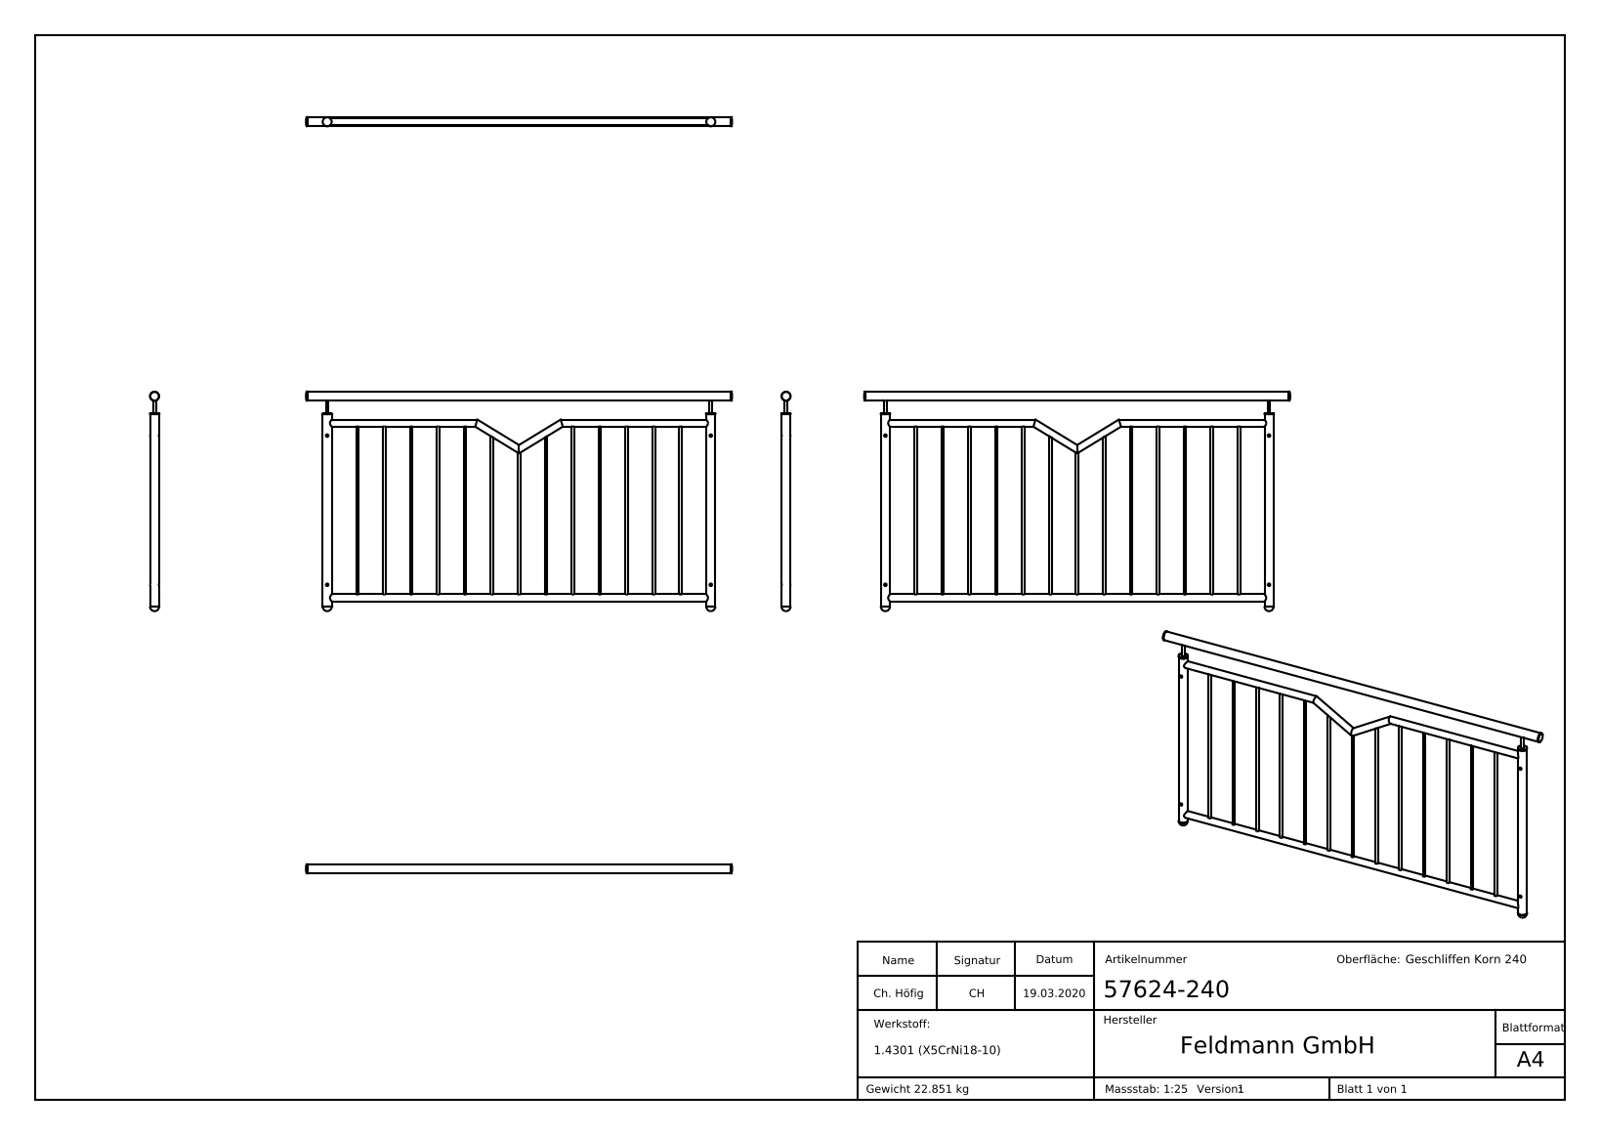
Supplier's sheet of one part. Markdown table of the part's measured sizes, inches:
| quantity | value |
| --- | --- |
| part name | Stopfen Konfig_50270-240G; Stopfen Konfig_50310-240G; 576XX-240 Teil1; Stopfen Konfig (+7 more) |
| STEP written by | SolidWorks 2015 (CONFIG_CONTROL_DESIGN) |
| units | inches |
| bodies | 10 solids, 6688 faces (3213 planar, 1051 cylindrical, 2424 other) |
| overall size | 633.953 × 314.961 × 314.961 |
| volume | 176.5 in³ |
| surface area | 3 255 in² |
| round holes (diameter × count) | 0.472 × 4, 1.169 × 4, 1.512 × 3, 0.268 × 2, 1.358 × 2, 1.362 × 1 |
| round bosses / shafts (diameter × count) | 0.472 × 15, 1.327 × 4, 1.669 × 3, 1.476 × 3, 0.315 × 2, 0.236 × 2 |
| partial cylindrical surfaces (radius × count) | 0.079 × 4, 0.764 × 3, 0.683 × 2, 0.76 × 1 |
| main face-to-face distances | 0.512, 0.197, 0.315, 35.063, 35.378, 35.575, 0.736, 0.738, 78.189, 0.739 |
| hole center spacings | 70.866, 27.559, 76.036, 4.969, 32.283, 37.252 |
